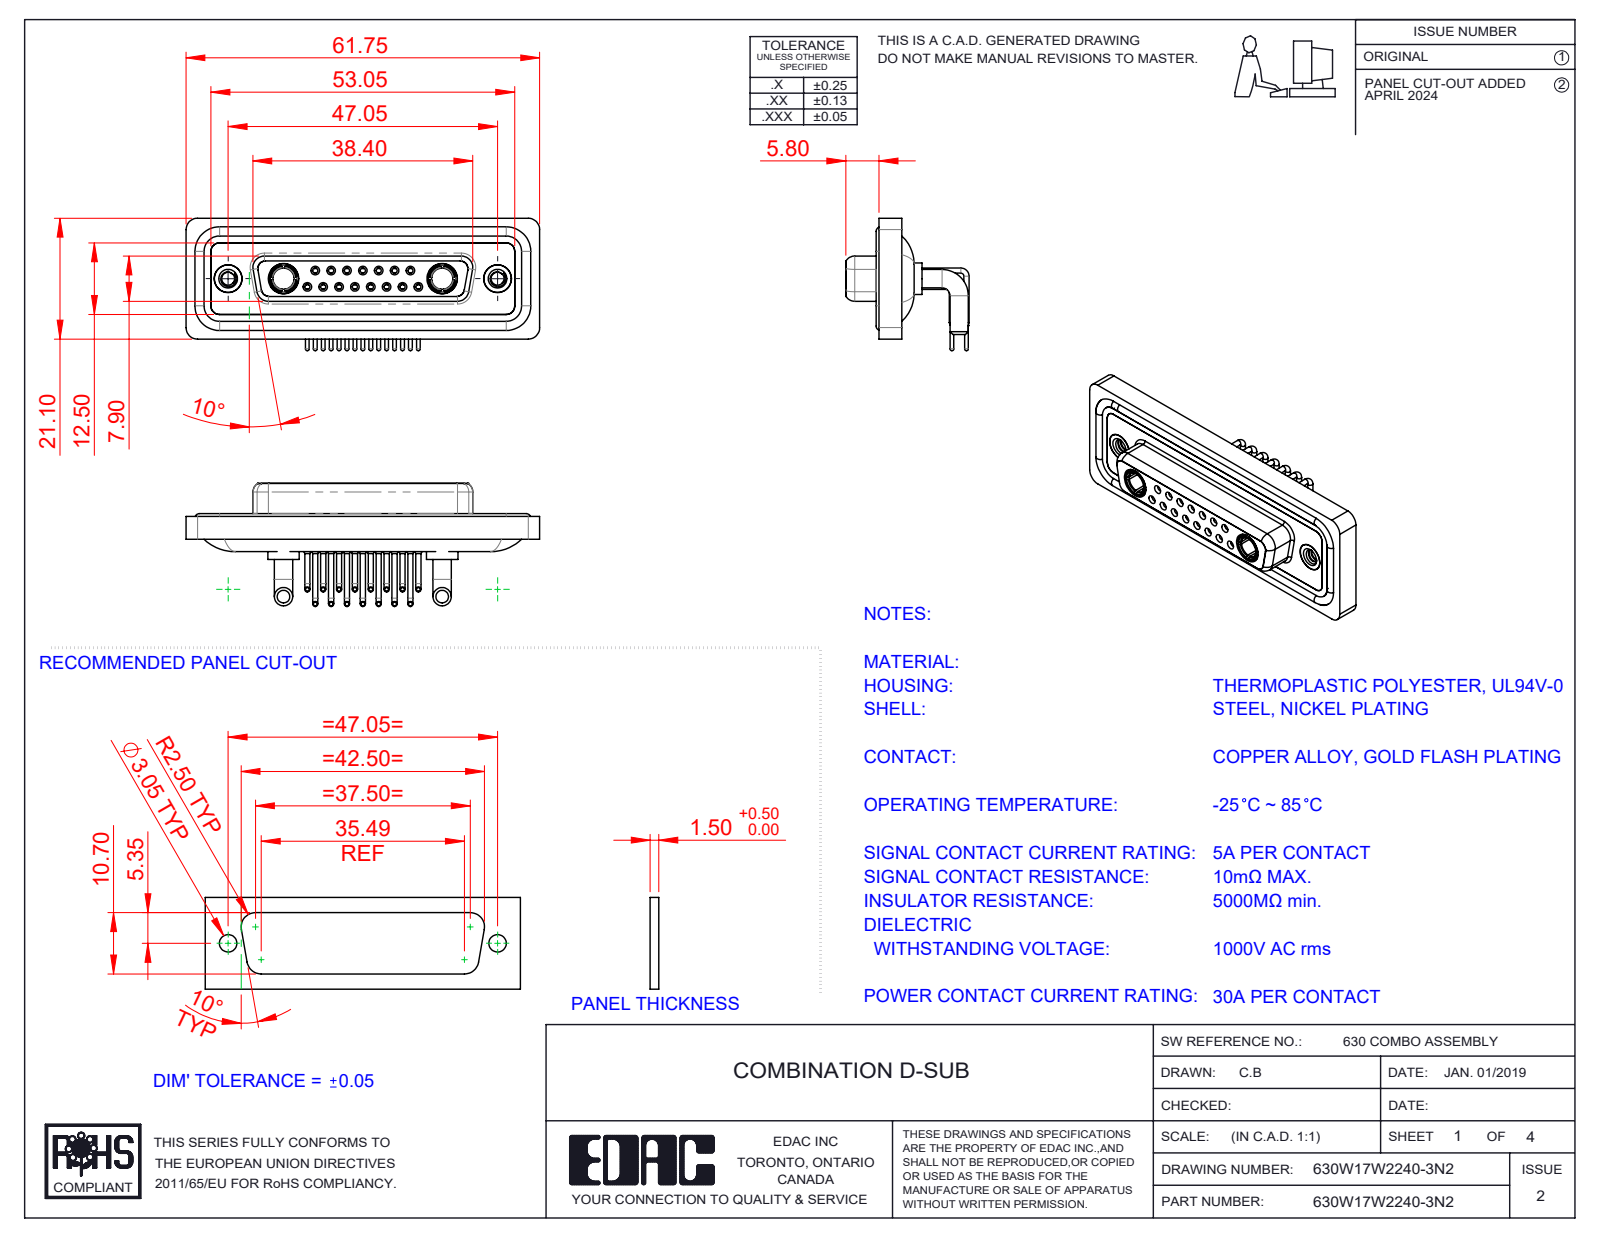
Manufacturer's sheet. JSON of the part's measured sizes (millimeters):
{"part_name": "630Combo Threaded Rivet_2; 630Combo Contact Row 1_50 Contacts; 630Combo Shell Rear_25 Contacts; Power Socket_30A RA (+5 more)", "step_written_by": "SolidWorks 2023 (CONFIG_CONTROL_DESIGN)", "units": "millimeters", "bodies": {"solids": 26, "faces": 1337, "planar": 388, "cylindrical": 583, "other": 366}, "overall_size": [61.75, 23.12, 21.53], "volume_mm3": 8543, "surface_area_mm2": 14567, "round_holes": [[0.9, 15], [1.1, 15], [1.5, 15], [2, 15], [1.6, 8], [1.7, 7], [4.85, 4], [2.26, 2], [3.7, 2], [4, 2], [4.05, 2], [5, 2]], "round_bosses_or_shafts": [[0.9, 15], [0.65, 15], [1.6, 11], [3.2, 4], [5.5, 2], [5.2, 2], [4.96, 2], [4.95, 2]], "partial_cylinders_radius": [[1.5, 18], [2, 18], [1.35, 8], [1.6, 8], [0.25, 4], [0.5, 4], [0.6, 4], [0.65, 4]], "face_to_face_distances": [0.4, 1.8, 4.1, 1.1, 1.6, 3.1, 2.5, 1.5, 3.7, 1.4], "hole_center_spacings": [3.16, 2.77, 5.54, 8.31, 5.04, 7.49, 11.08, 5.03]}
